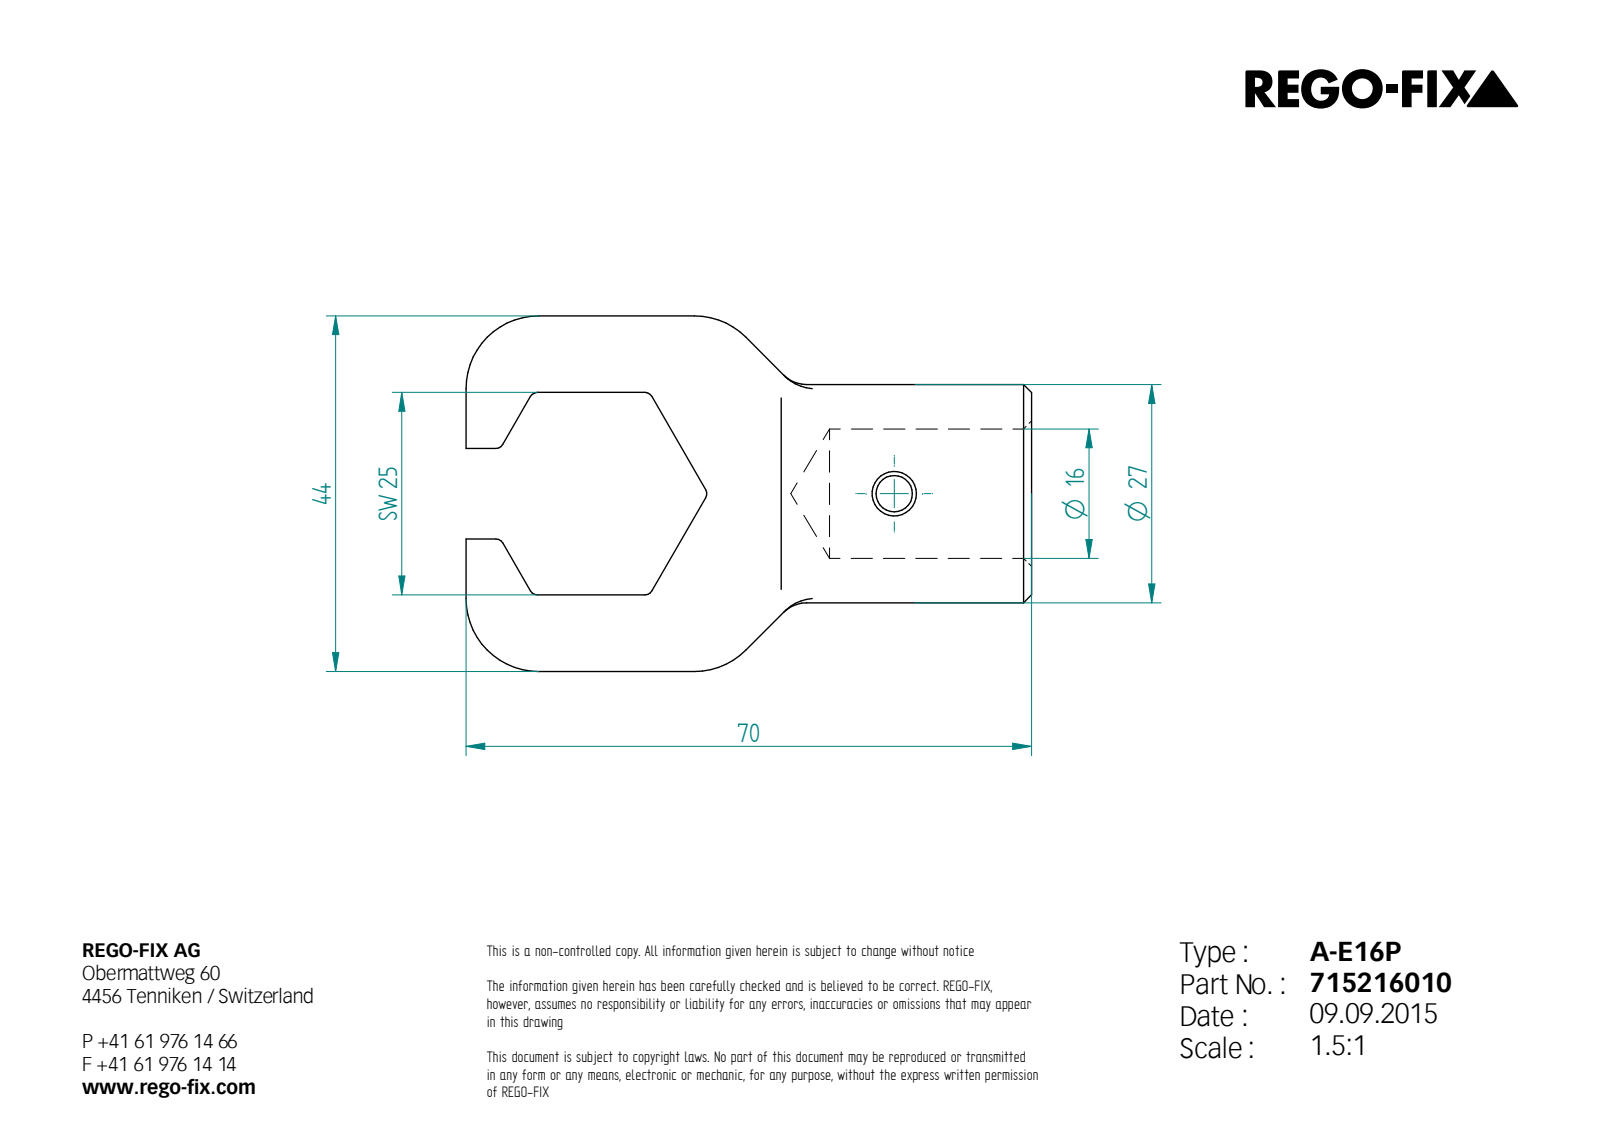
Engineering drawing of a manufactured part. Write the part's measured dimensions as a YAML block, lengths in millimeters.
step_written_by: "Unknown (AUTOMOTIVE_DESIGN)"
units: millimeters
bodies: {solids: 1, faces: 53, planar: 19, cylindrical: 22, other: 12}
overall_size: [70, 44, 27]
volume: 18431
surface_area: 8142
round_holes:
  - {diameter: 4.5, count: 1}
  - {diameter: 5.5, count: 1}
  - {diameter: 16, count: 1}
round_bosses_or_shafts:
  - {diameter: 27, count: 1}
partial_cylinders:
  - {radius: 1, count: 13}
  - {radius: 9, count: 4}
face_to_face_distances: [6, 31, 9.47, 34.53, 44, 39, 70, 25.04, 25.06, 16.4]
